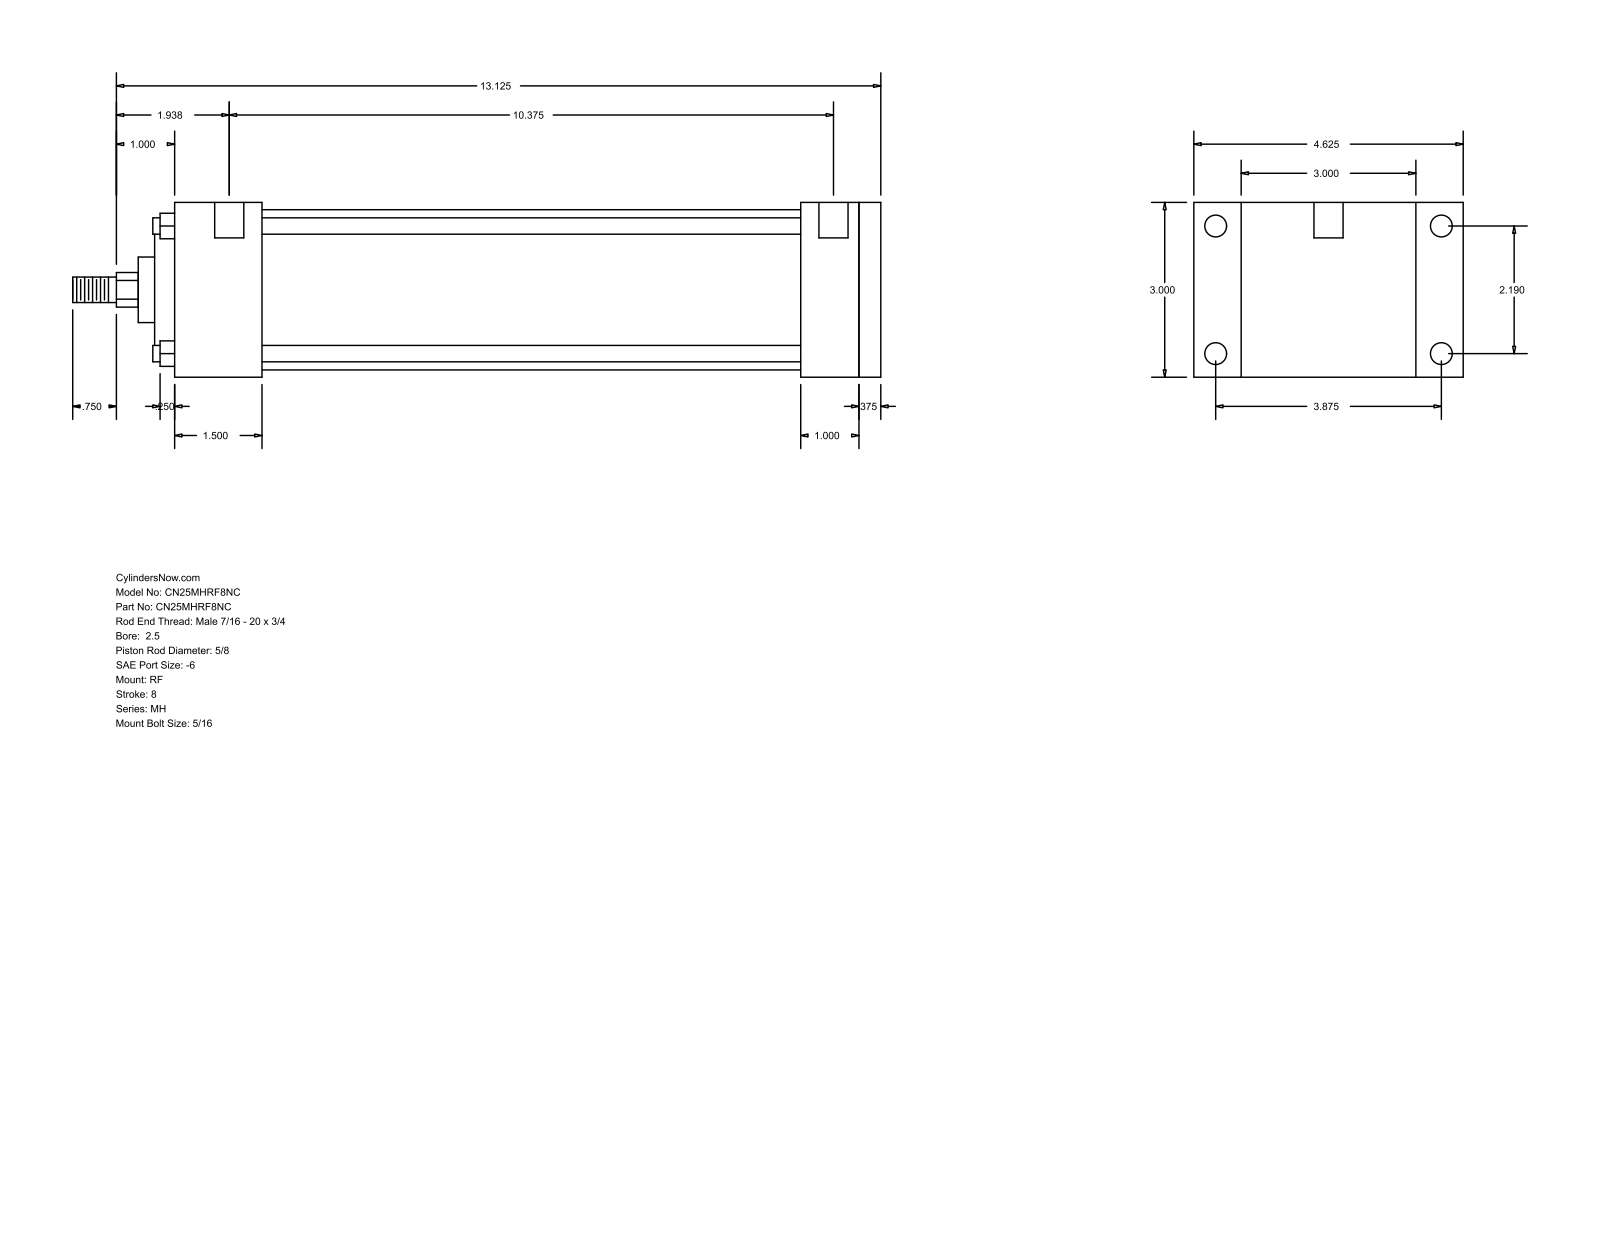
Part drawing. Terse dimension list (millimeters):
name: MH_RF__0250_0.625
written by: GSSL Pune (CONFIG_CONTROL_DESIGN)
unit: mm
bodies: 0 solids, 94 faces (65 planar, 29 cylindrical, 0 other)
size: 352.43 × 117.47 × 76.2
holes: 4× ⌀5.56, 4× ⌀9.53, 2× ⌀12.7
bosses: 4× ⌀7.14, 1× ⌀69.85, 1× ⌀55.55, 1× ⌀28.57, 1× ⌀15.88, 1× ⌀11.11
rounds: 1× R7.54
face distances: 76.2, 9.53, 307.98, 298.45, 25.4, 34.93, 38.1, 273.05, 234.95, 260.35
hole spacings: 55.62, 98.42, 113.05, 271.46, 3.17, 4.76, 263.53, 266.7
